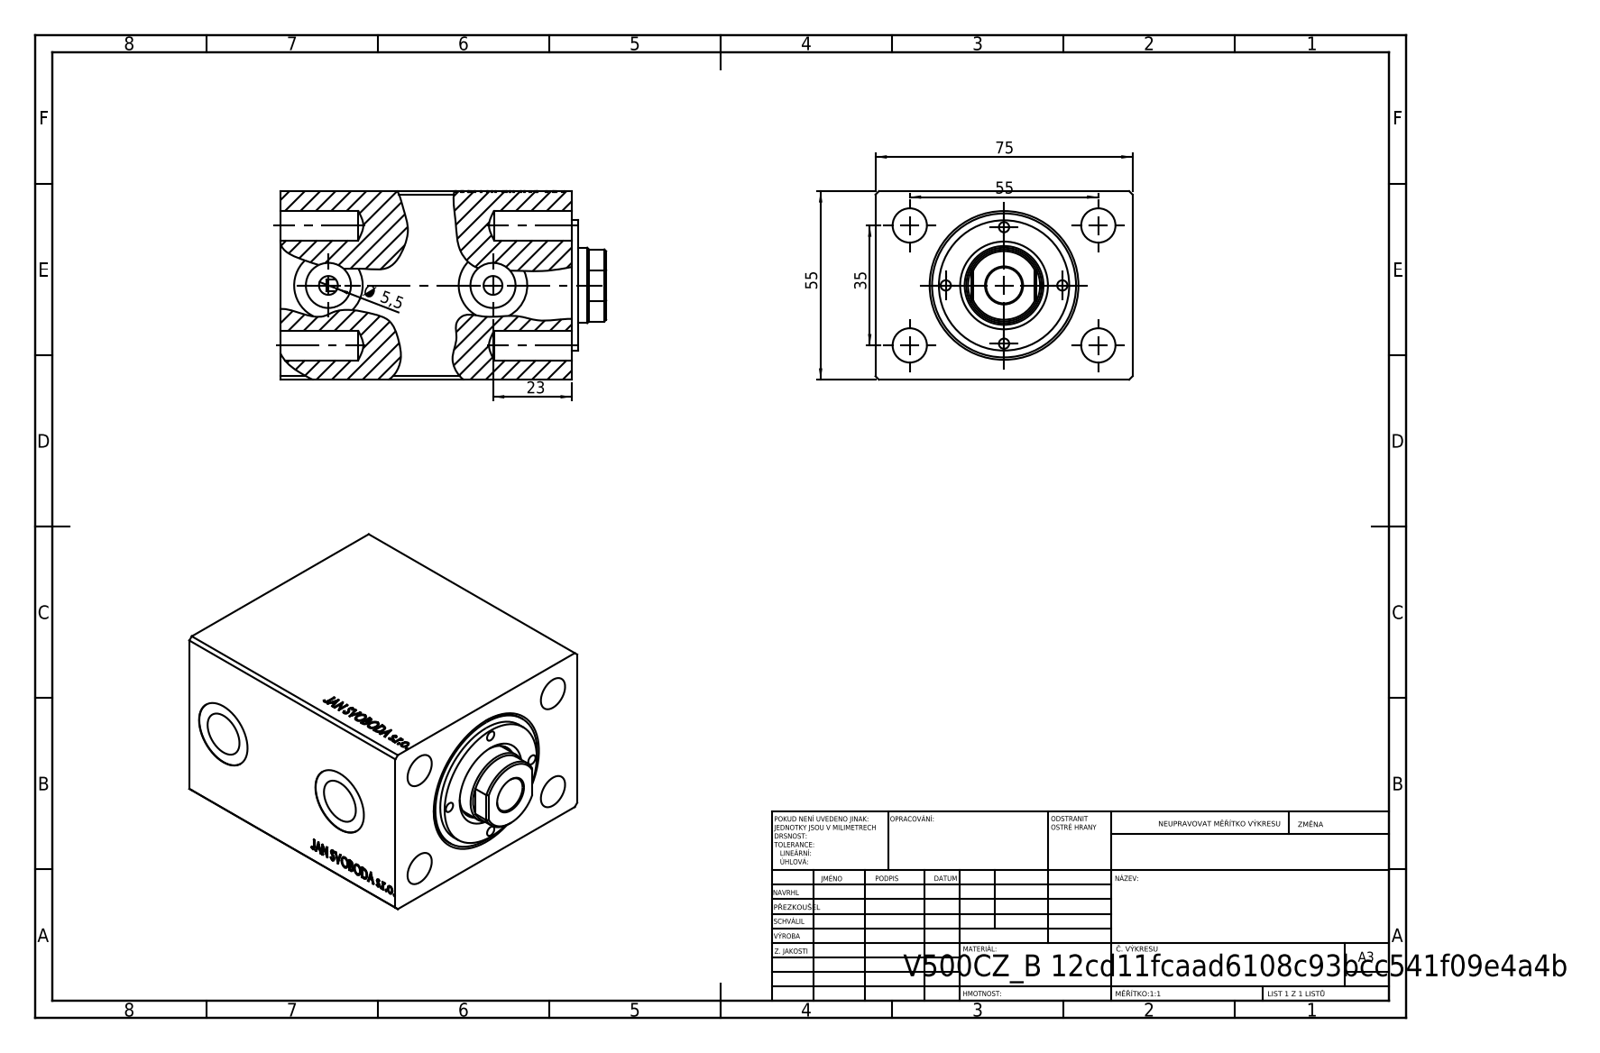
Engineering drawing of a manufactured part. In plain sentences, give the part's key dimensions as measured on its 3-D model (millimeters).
The part is named "V500CZ_B_VC; V500CZ". Its 3-D file was written by "SolidWorks 2019 (CONFIG_CONTROL_DESIGN)". It is 3 solids with 873 faces: 399 planar, 58 cylindrical and 416 other. Overall it measures 95 by 75 by 55 millimeters. Its volume is 341 694 cubic millimeters and its surface area 70 986 square millimeters. Round holes: 4 of diameter 3, 4 of diameter 10, 2 of diameter 5.5, 2 of diameter 13.16, 2 of diameter 20, 1 of diameter 10.5, 1 of diameter 22, 1 of diameter 23, 1 of diameter 32, 1 of diameter 36, 1 of diameter 42. Round bosses or shafts: 1 of diameter 38. Partial cylindrical surfaces (rounded edges, fillets, slot ends): 1 of radius 10.5. The main face-to-face distances are 55, 75, 85, 13.5, 71.5, 6.5, 65, 20, 84.8, 19.8. The hole center spacings are 17, 20.41, 24.04, 27.5, 32.6, 44.12, 47.82, 34.
